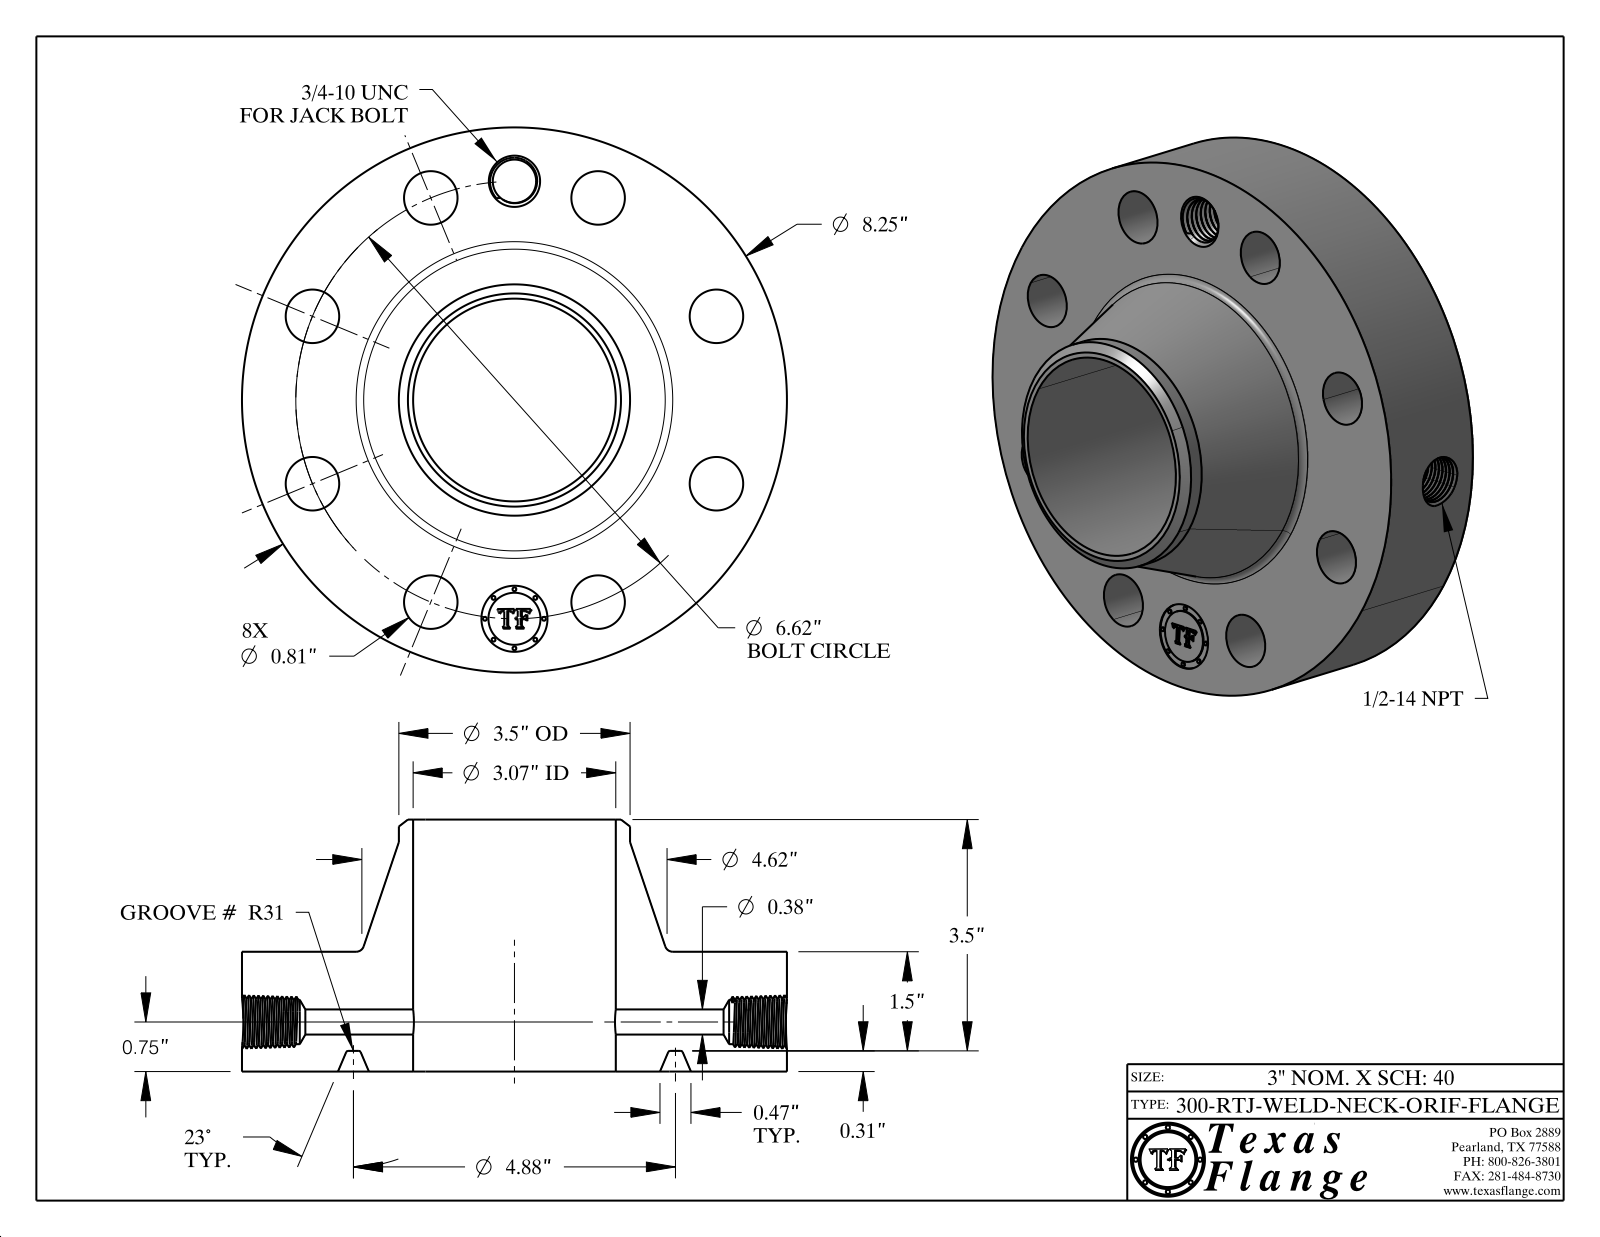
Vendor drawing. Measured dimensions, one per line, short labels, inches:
name: 300-RTJ-WELD-NECK
written by: CATIA V5 STEP AP214 (AUTOMOTIVE_DESIGN)
unit: in
bodies: 1 solid, 795 faces (370 planar, 96 cylindrical, 329 other)
size: 8.25 × 8.25 × 3.813
volume: 82.62 in³; area: 243.9 in²
holes: 8× ⌀0.81, 1× ⌀0.38, 1× ⌀0.656, 1× ⌀0.672, 1× ⌀1, 1× ⌀3.068
bosses: 8× ⌀0.061, 1× ⌀8.25, 1× ⌀3.5, 1× ⌀0.788
face distances: 1.813, 0.313, 1.5, 3.813, 3.5, 2, 0.015, 1.798, 1.485, 2.015
hole spacings: 3.31, 4.681, 6.116, 6.62, 1.291, 2.533, 2.533, 3.678
